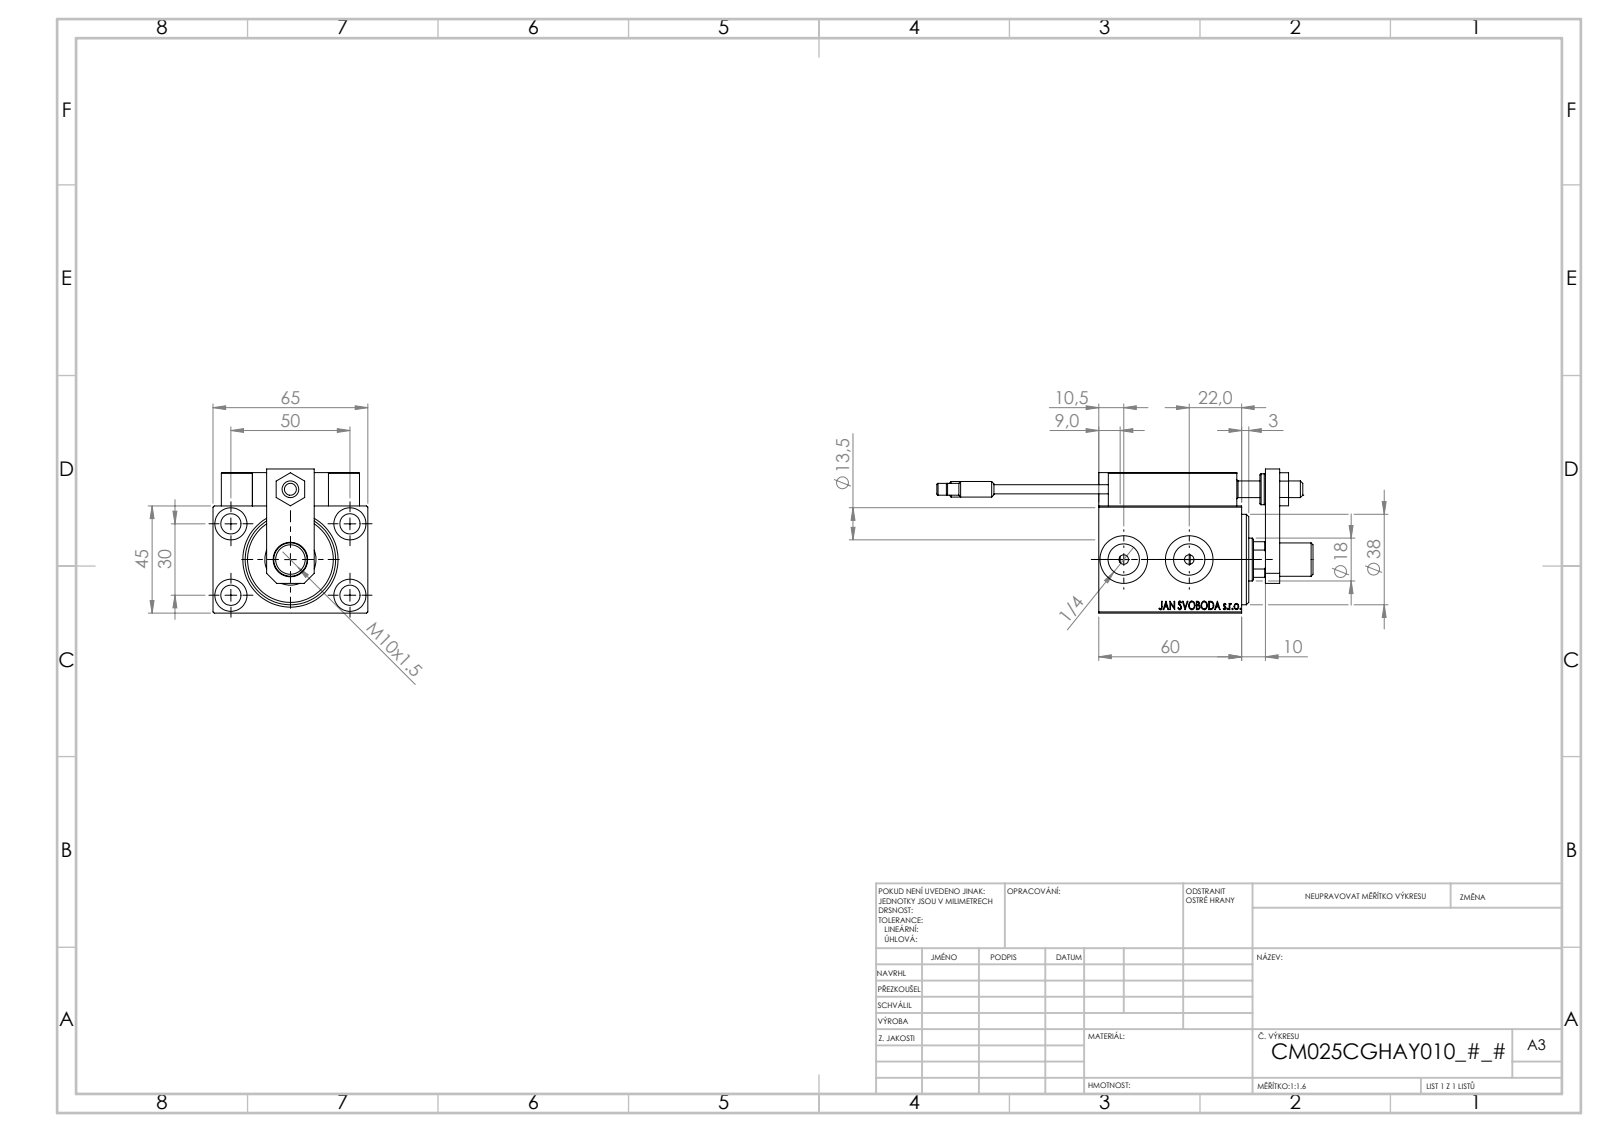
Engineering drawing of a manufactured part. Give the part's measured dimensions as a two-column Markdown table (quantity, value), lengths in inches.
| quantity | value |
| --- | --- |
| part name | KONCOVKA_Y; TYC_L79; ZARAZKA; ALLEN BOLT D5 (+7 more) |
| STEP written by | SolidWorks 2019 (CONFIG_CONTROL_DESIGN) |
| units | inches |
| bodies | 24 solids, 1318 faces (566 planar, 200 cylindrical, 552 other) |
| overall size | 6.22 × 2.559 × 2.382 |
| volume | 12.32 in³ |
| surface area | 104 in² |
| round holes (diameter × count) | 0.157 × 6, 0.315 × 5, 0.335 × 5, 0.126 × 4, 0.531 × 4, 0.197 × 2, 0.518 × 2, 0.787 × 2, 0.276 × 1, 0.571 × 1, 0.709 × 1, 0.846 × 1 |
| round bosses / shafts (diameter × count) | 0.197 × 4, 0.256 × 2, 0.15 × 2, 0.551 × 1, 0.512 × 1, 0.472 × 1, 0.433 × 1 |
| partial cylindrical surfaces (radius × count) | 0.012 × 30, 0.118 × 2, 0.335 × 1 |
| main face-to-face distances | 1.772, 0.394, 0.276, 0.551, 2.323, 0.118, 0.512, 2.559, 0.236, 0.354 |
| hole center spacings | 1.148, 0.448, 0.479, 0.787, 0.987, 1.138, 1.165, 1.169 |
